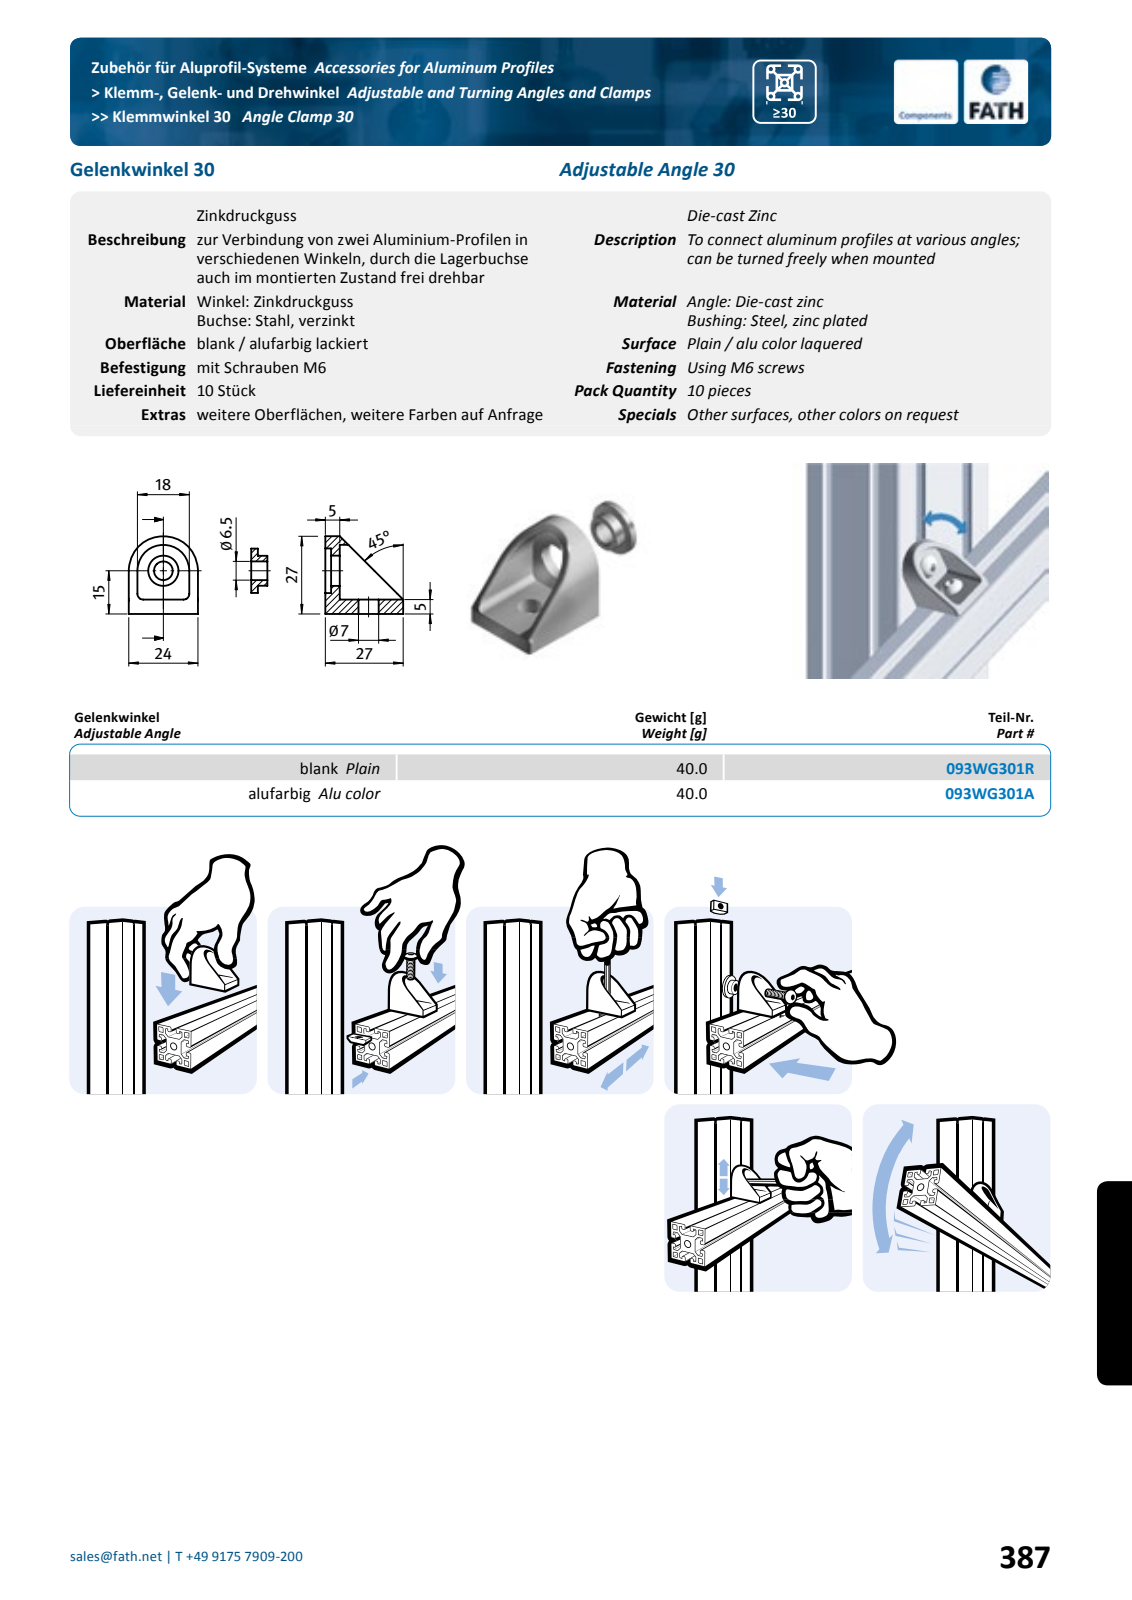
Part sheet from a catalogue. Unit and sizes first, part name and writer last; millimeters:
Units: millimetres
Overall size (bounding box): 27.3 × 27 × 24
Round holes (diameter × count): ⌀6.5 ×1, ⌀7 ×1, ⌀10.5 ×1, ⌀15.5 ×1
Round bosses / shafts (diameter × count): ⌀15.4 ×1, ⌀10.4 ×1
Partial cylindrical surfaces — rounded edges, fillets, slot ends (radius × count): R1 ×7
Main face-to-face distances: 5, 2, 3, 5.3, 2.3, 27.3, 27, 25, 22, 5.6
Volume: 6 522 mm³ · Surface area: 4 349 mm²
Bodies: 2 solids, 59 faces (14 planar, 19 cylindrical, 26 other)
Part name (STEP PRODUCT): fath_093wg301a_1; fath_093wg301a_2
STEP written by: Spatial InterOp 3D (automotive_design)
